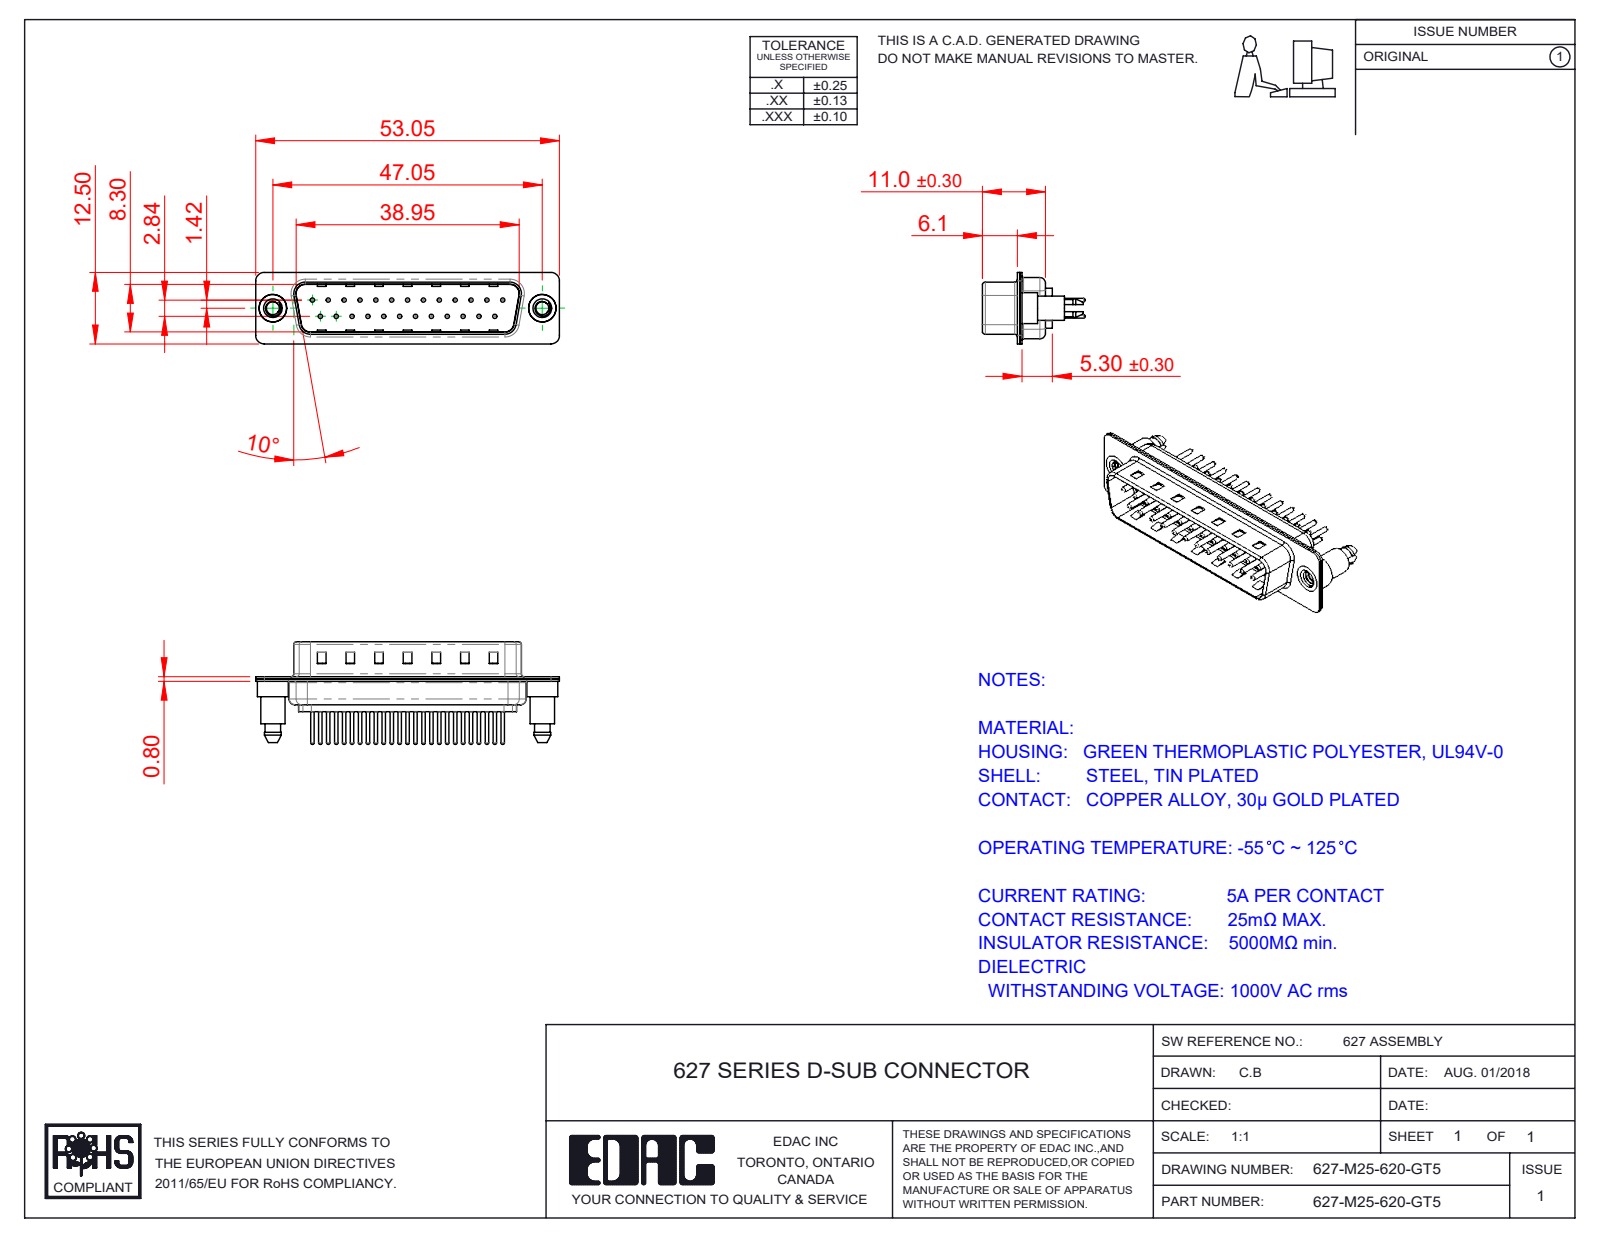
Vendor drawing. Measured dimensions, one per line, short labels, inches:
name: 627M Contact Row 1_20; 627M Housing_25 Contacts; 627M 4-40 Threaded Boardlock; 627M Shell Front_25 Contacts (+3 more)
written by: SolidWorks 2020 (CONFIG_CONTROL_DESIGN)
unit: in
bodies: 30 solids, 1351 faces (362 planar, 519 cylindrical, 470 other)
size: 2.089 × 0.705 × 0.492
volume: 0.174 in³; area: 11.12 in²
holes: 25× ⌀0.03, 25× ⌀0.063, 25× ⌀0.079, 2× ⌀0.089, 2× ⌀0.157, 2× ⌀0.189
bosses: 25× ⌀0.059, 25× ⌀0.024, 2× ⌀0.213, 2× ⌀0.193, 2× ⌀0.167
rounds: 18× R0.059, 12× R0.079, 10× R0.063, 8× R0.02, 4× R0.01, 4× R0.024, 4× R0.026, 4× R0.035
face distances: 0.016, 0.031, 0.374, 0.358, 0.343, 0.39, 0.047, 0.24, 0.224, 0.03
hole spacings: 0.124, 0.109, 0.218, 0.327, 0.436, 0.545, 0.654, 0.198
